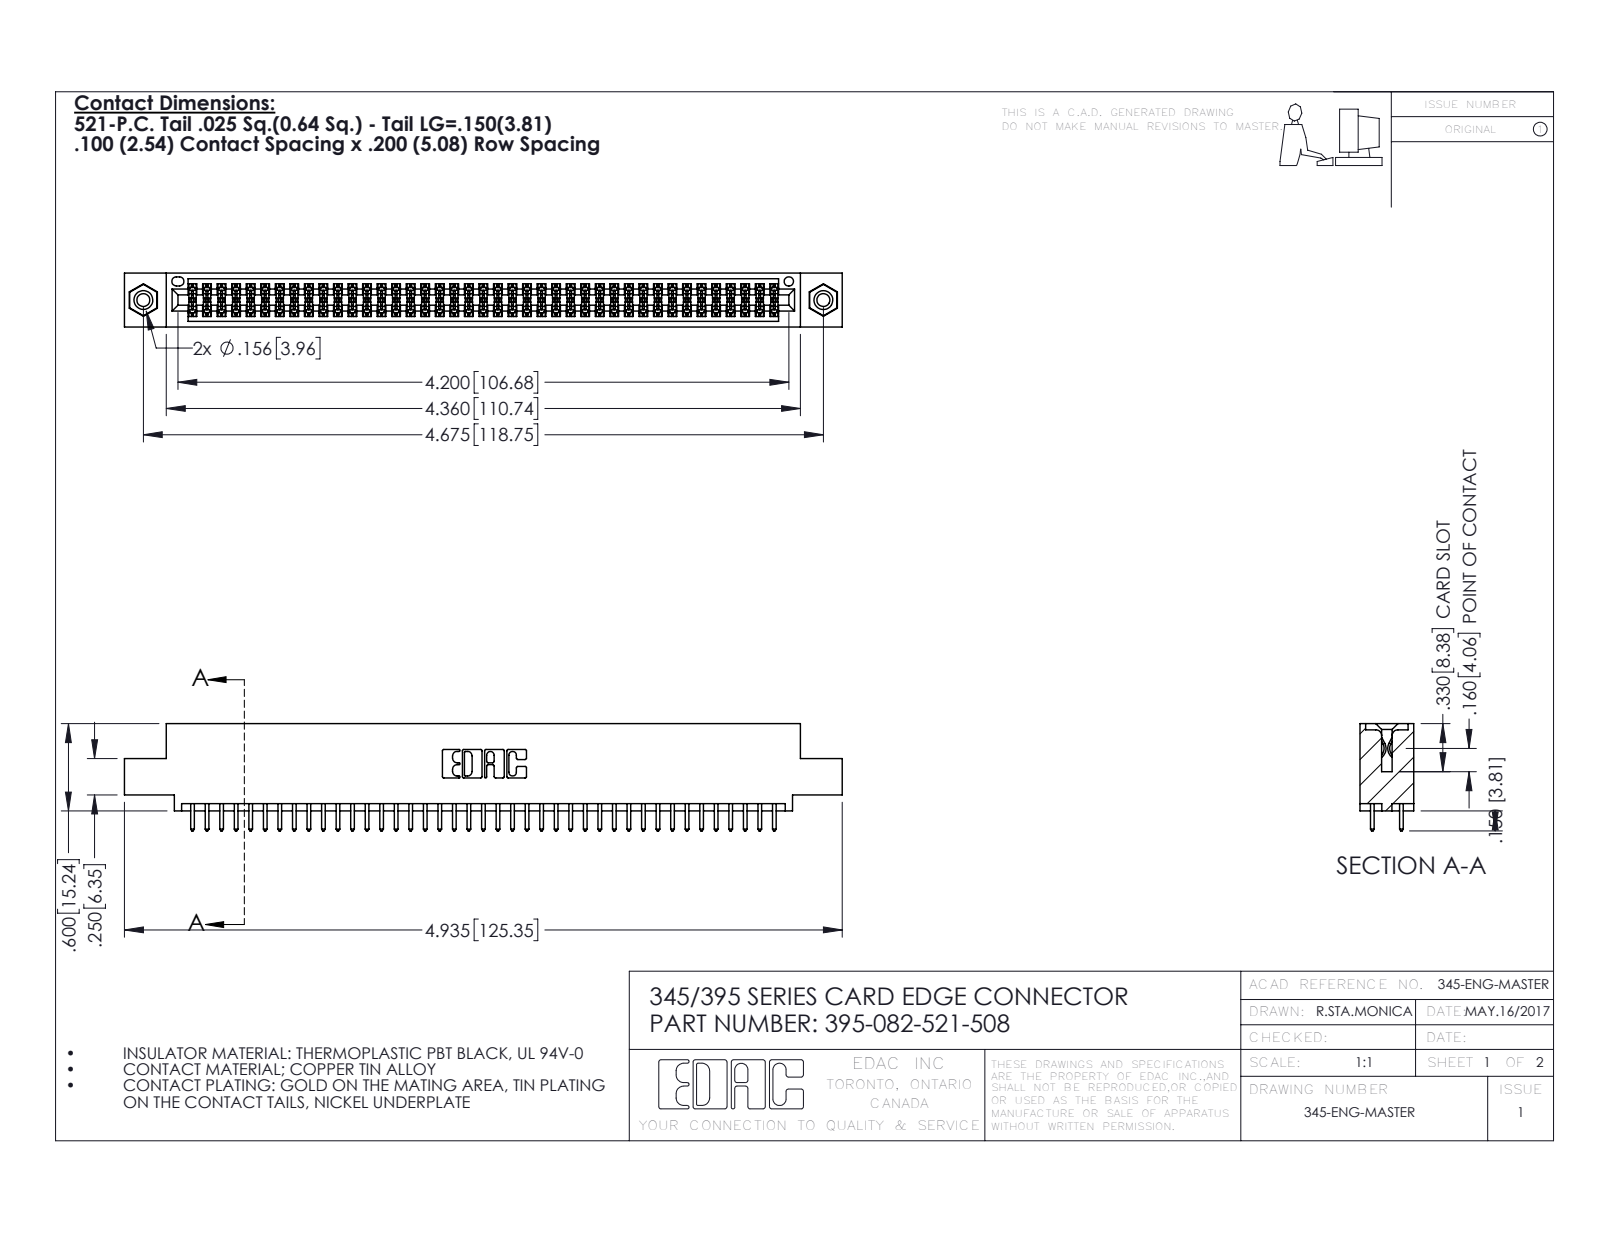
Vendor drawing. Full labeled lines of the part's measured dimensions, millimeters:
Part name (STEP PRODUCT): 345-292-001_345-293-121; 395-082-521-508; 345-250-001_345-250-003-102; 345 Part_0.110 Offset - 0.156 Dia-TI
STEP written by: SolidWorks 2016 (CONFIG_CONTROL_DESIGN)
Units: millimetres
Bodies: 85 solids, 4290 faces (2822 planar, 1452 cylindrical, 16 other)
Overall size (bounding box): 125.3 × 18.7 × 9.4
Volume: 12 100 mm³ · Surface area: 17 680 mm²
Round holes (diameter × count): ⌀2.3 ×2, ⌀3.2 ×2, ⌀4 ×2, ⌀1.6 ×1
Round bosses / shafts (diameter × count): ⌀3.9 ×2
Partial cylindrical surfaces — rounded edges, fillets, slot ends (radius × count): R0.2 ×123, R0.3 ×82, R0.3 ×22, R0.2 ×6, R0.8 ×6, R0.7 ×3, R0.4 ×2, R0.5 ×2
Main face-to-face distances: 1.8, 7.6, 5.1, 9.4, 2.5, 6.9, 0.6, 5.7, 4.4, 3.8
Hole centre spacings: 6.9, 112.8, 118.7
